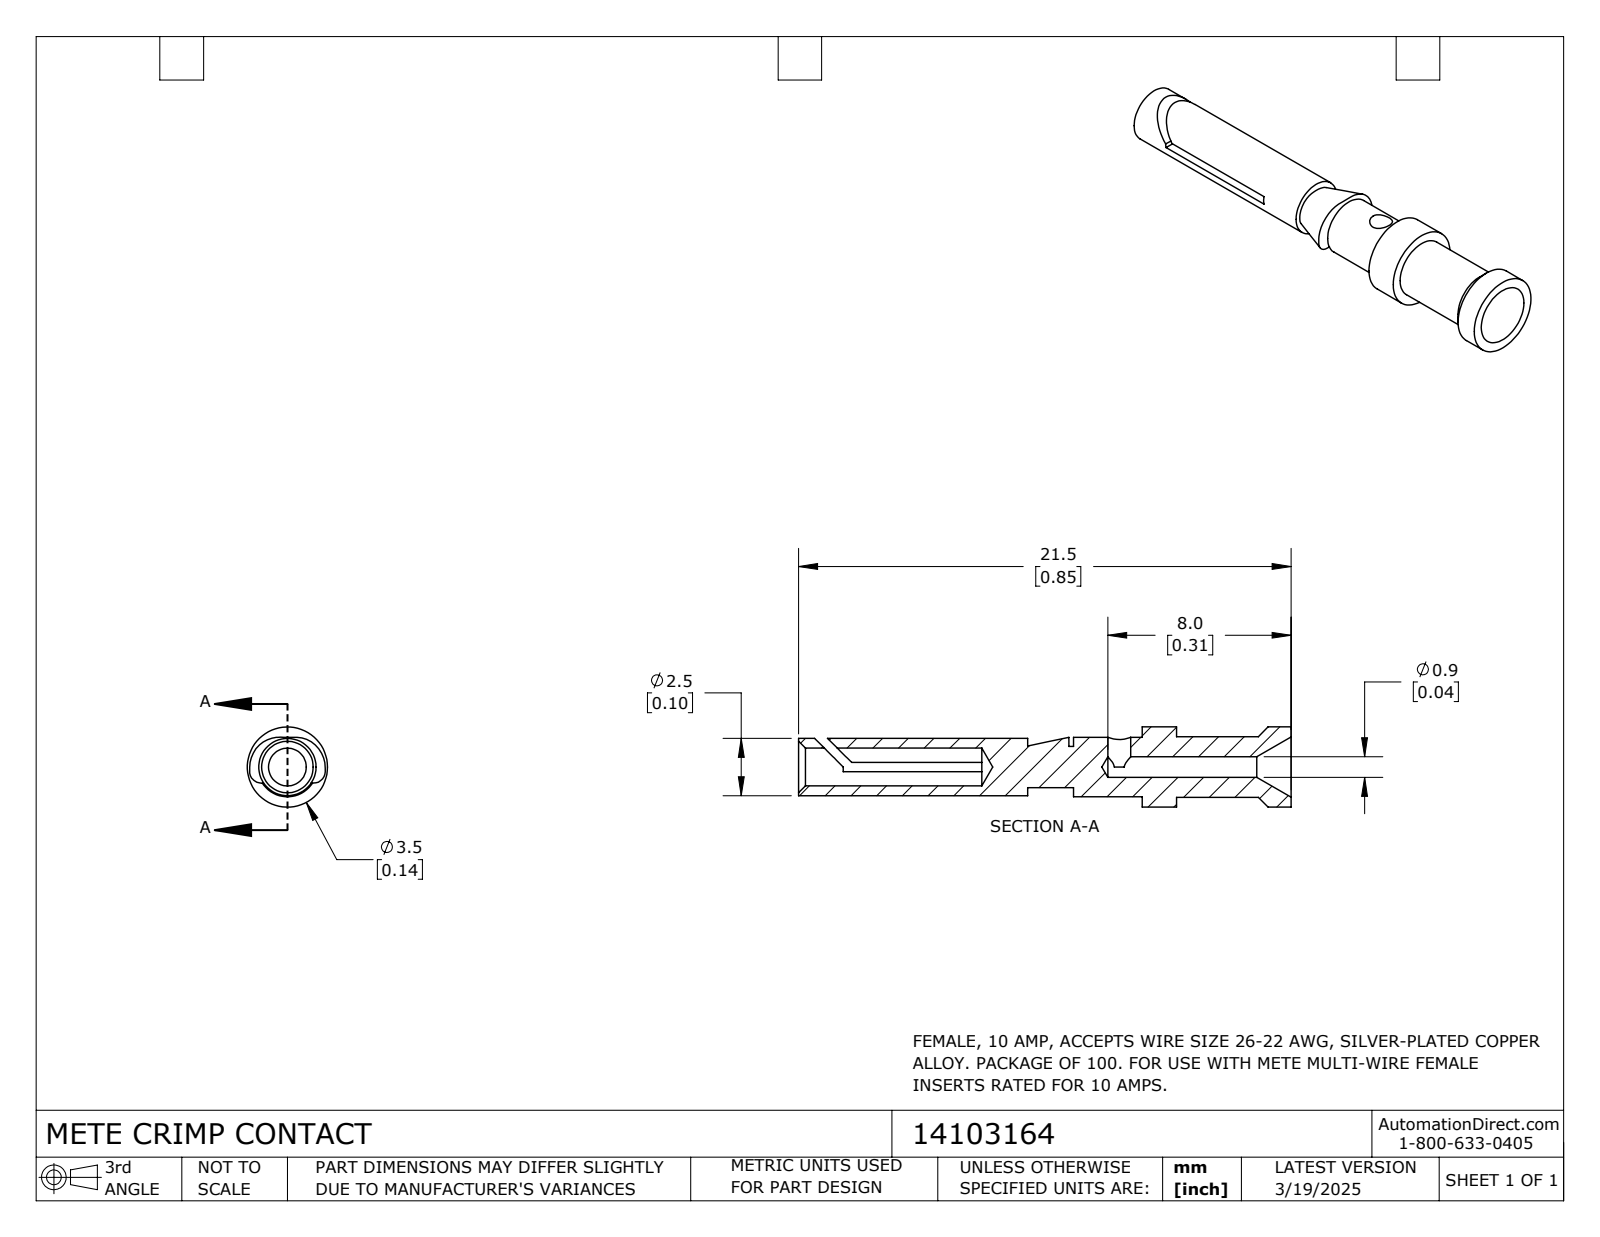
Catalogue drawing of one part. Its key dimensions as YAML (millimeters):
part_name: "14103164"
step_written_by: "SolidWorks 2024 (CONFIG_CONTROL_DESIGN)"
units: millimeters
bodies: {solids: 1, faces: 52, planar: 19, cylindrical: 22, other: 11}
overall_size: [21.5, 3.5, 3.5]
volume: 91
surface_area: 279
round_holes:
  - {diameter: 0.9, count: 1}
  - {diameter: 1, count: 1}
  - {diameter: 1.65, count: 1}
round_bosses_or_shafts:
  - {diameter: 3.5, count: 1}
  - {diameter: 2.65, count: 1}
  - {diameter: 2.6, count: 1}
  - {diameter: 2.5, count: 1}
  - {diameter: 1.8, count: 1}
face_to_face_distances: [0.4, 6.5, 5, 1.5, 9.7, 4.7, 3.2, 9.5, 4.5, 3]
